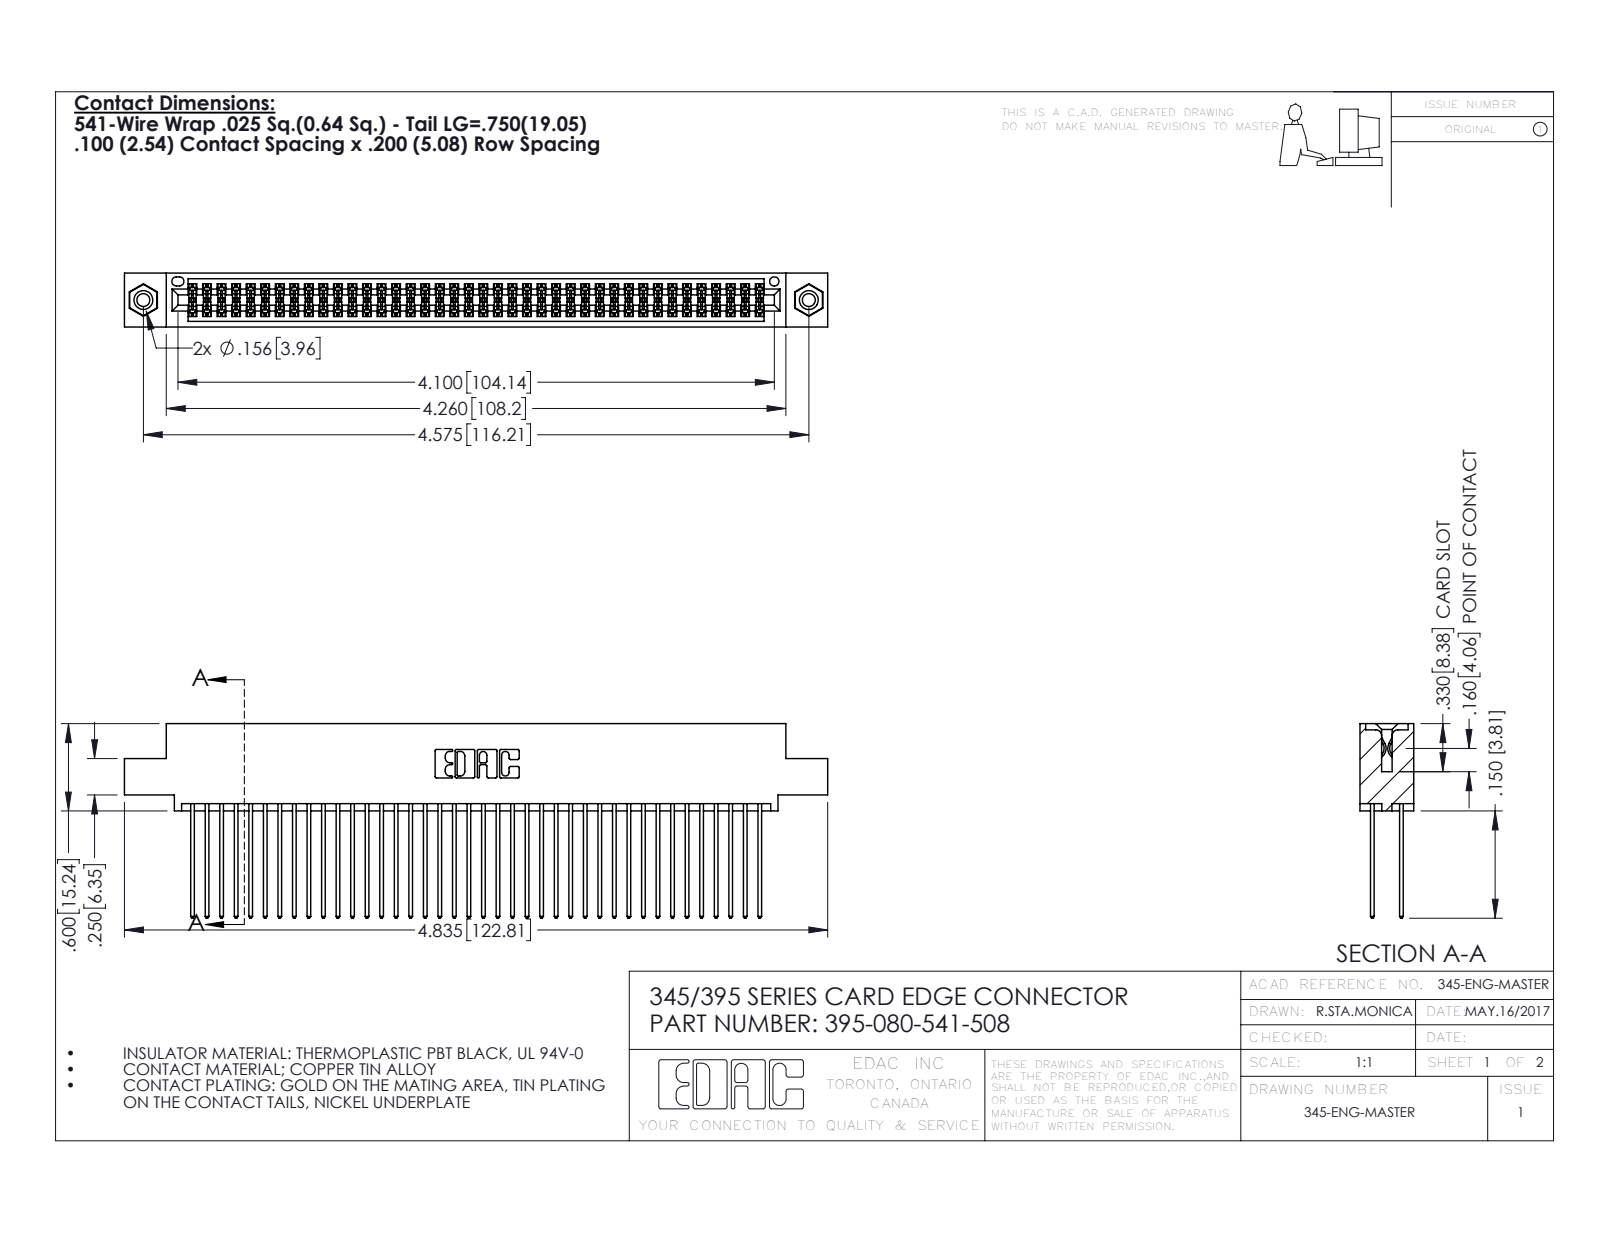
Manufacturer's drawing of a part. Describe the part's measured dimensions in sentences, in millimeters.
The part is named "345-250-001_345-250-003-102; 345 Part_0.110 Offset - 0.156 Dia-TI; 345-292-001_345-293-141; 395-080-541-508". Its 3-D file was written by "SolidWorks 2016 (CONFIG_CONTROL_DESIGN)". It is 83 solids with 4190 faces: 2756 planar, 1418 cylindrical and 16 other. Overall it measures 122.8 by 34 by 9.4 millimeters. Its volume is 12 300 cubic millimeters and its surface area 20 390 square millimeters. Round holes: 2 of diameter 2.3, 2 of diameter 3.2, 2 of diameter 4, 1 of diameter 1.6. Round bosses or shafts: 2 of diameter 3.9. Partial cylindrical surfaces (rounded edges, fillets, slot ends): 120 of radius 0.2, 80 of radius 0.3, 22 of radius 0.3, 6 of radius 0.2, 6 of radius 0.8, 3 of radius 0.7, 2 of radius 0.4, 2 of radius 0.5. The main face-to-face distances are 1.8, 7.6, 5.1, 2.5, 6.9, 0.6, 5.7, 9.4, 4.4, 3.8. The hole center spacings are 6.9, 110.2, 116.2.
